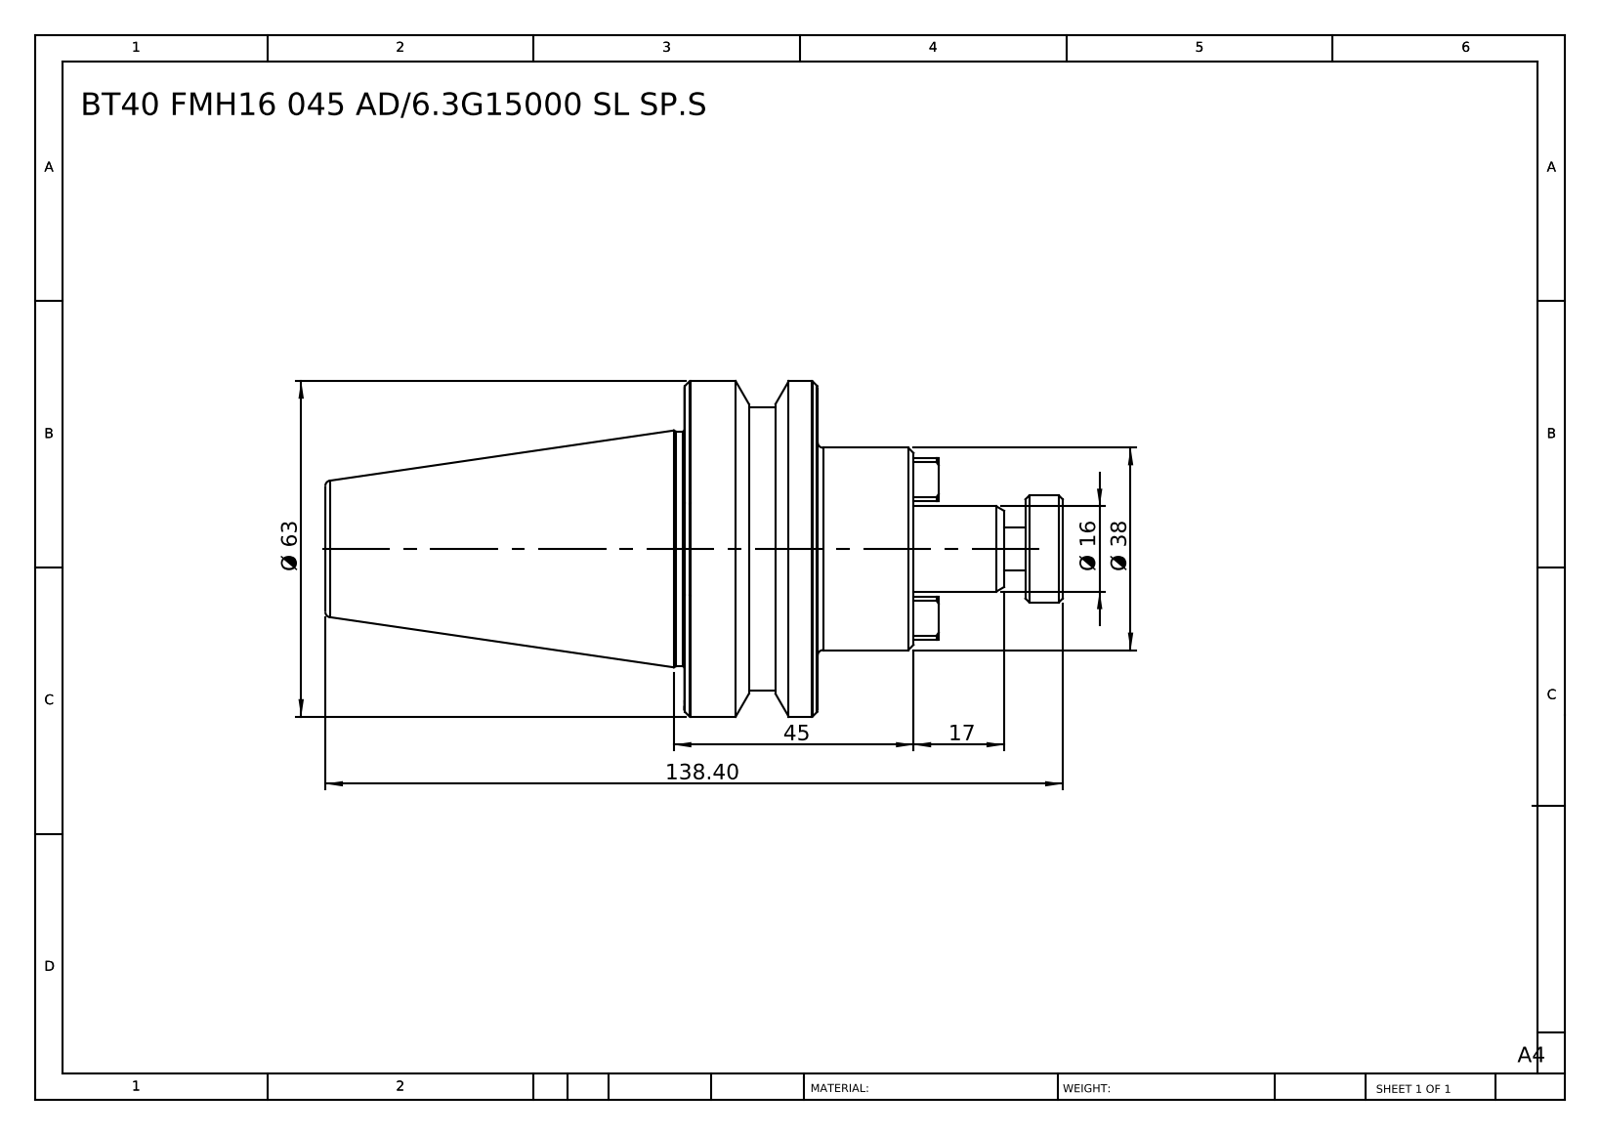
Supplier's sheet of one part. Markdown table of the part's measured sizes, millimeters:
| quantity | value |
| --- | --- |
| part name | BT40 FMH16 045 AD-6.3G15000 SL SP.S |
| STEP written by | SolidWorks 2014 (CONFIG_CONTROL_DESIGN) |
| units | millimeters |
| bodies | 1 solid, 91 faces (35 planar, 16 cylindrical, 40 other) |
| overall size | 138.4 × 63 × 63 |
| volume | 165 101 mm³ |
| surface area | 22 474 mm² |
| round bosses / shafts (diameter × count) | 63 × 1, 53 × 1, 44 × 1, 38 × 1, 20 × 1, 16 × 1, 8 × 1 |
| main face-to-face distances | 25, 18, 43, 110.4, 92.4, 67.4, 28, 46, 71, 138.4 |
